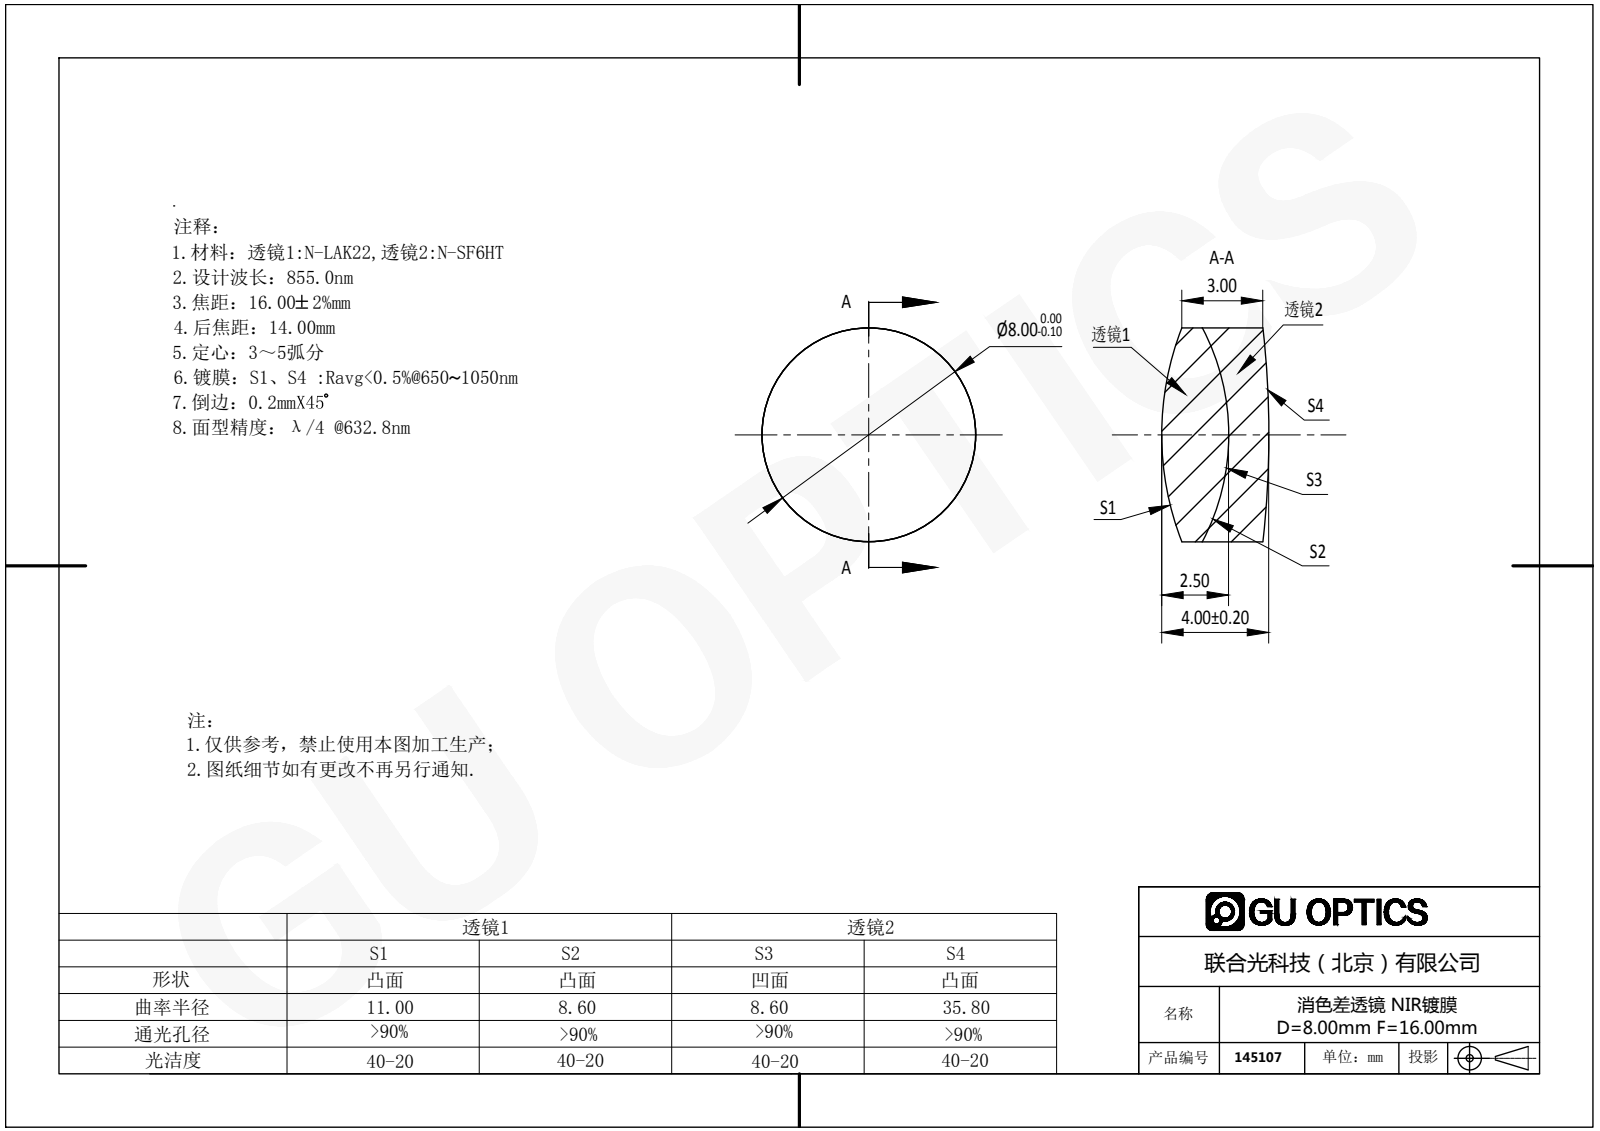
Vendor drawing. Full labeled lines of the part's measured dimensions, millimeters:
Part name (STEP PRODUCT): 145107
STEP written by: SolidWorks 2016 (AUTOMOTIVE_DESIGN)
Units: millimetres
Bodies: 2 solids, 12 faces (0 planar, 4 cylindrical, 8 other)
Overall size (bounding box): 8 × 8 × 4
Volume: 177 mm³ · Surface area: 285 mm²
Round bosses / shafts (diameter × count): ⌀8 ×1
